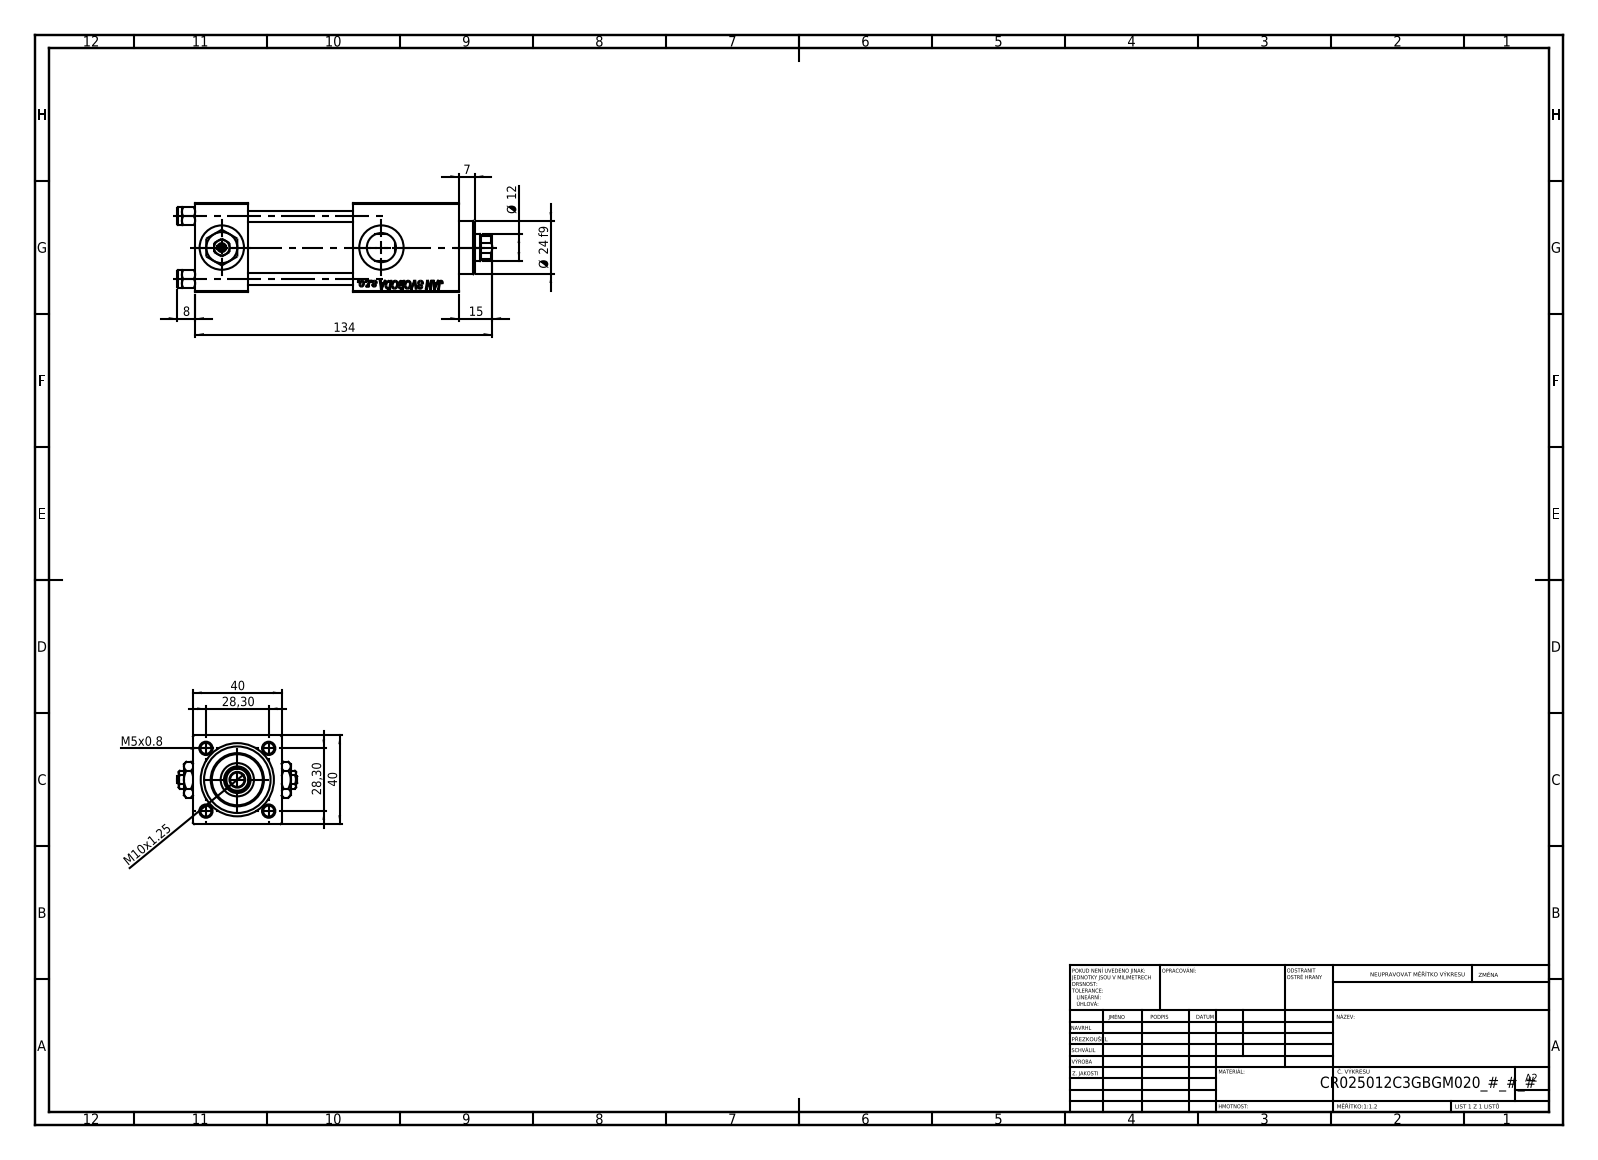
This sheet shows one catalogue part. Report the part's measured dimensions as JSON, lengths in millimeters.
{"part_name": "NUT_M5_C; V215_VC_A; V215CR_C_Body; V215CR_VCP_C (+2 more)", "step_written_by": "SolidWorks 2019 (CONFIG_CONTROL_DESIGN)", "units": "millimeters", "bodies": {"solids": 13, "faces": 1248, "planar": 572, "cylindrical": 98, "other": 578}, "overall_size": [142, 54, 40], "volume_mm3": 140985, "surface_area_mm2": 56209, "round_holes": [[5, 4], [20, 3], [7, 2], [13.16, 2], [6.5, 1], [12, 1], [15, 1], [25, 1], [30, 1]], "round_bosses_or_shafts": [[8, 4], [31, 1], [24, 1]], "partial_cylinders_radius": [[5.5, 1]], "face_to_face_distances": [40, 24, 39.8, 90.3, 66.3, 48, 47, 71, 19.3, 119], "hole_center_spacings": [20.01, 28.3, 40.02, 72]}
